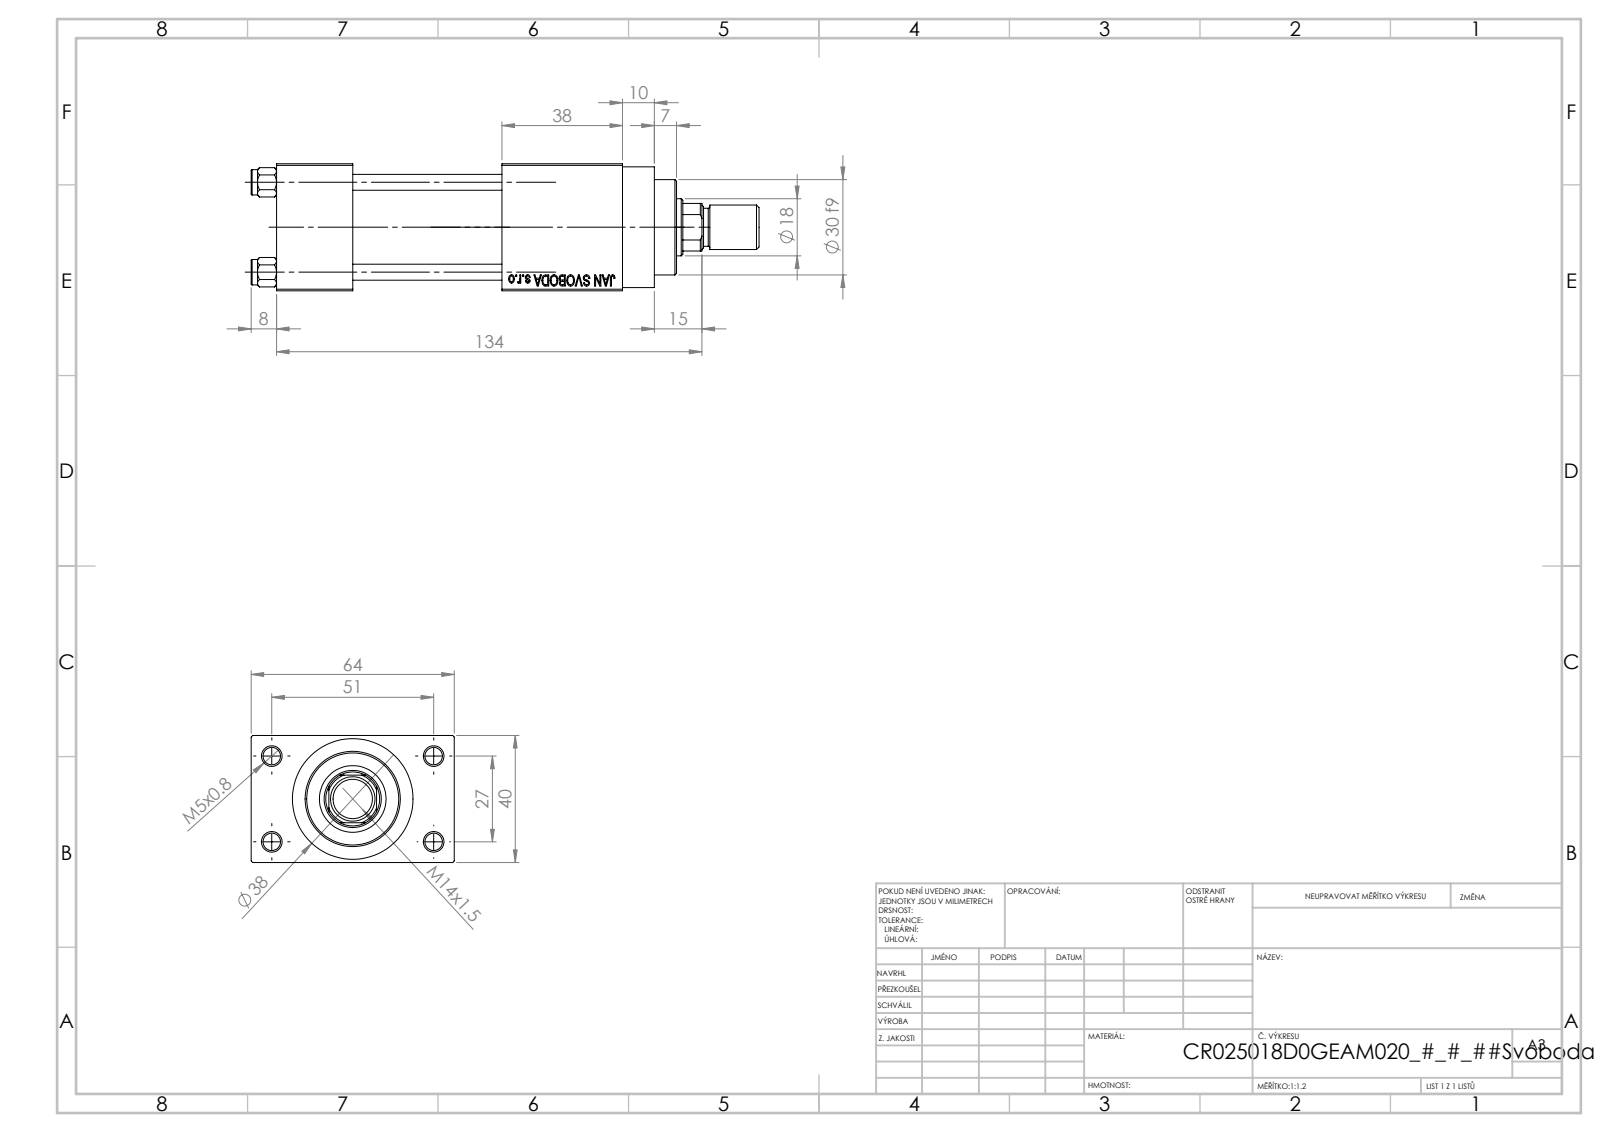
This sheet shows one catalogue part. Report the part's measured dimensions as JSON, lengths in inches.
{"part_name": "ROD_END_AH; NUT_M5_D; V215CR_VCP_D; V215_VC_A (+2 more)", "step_written_by": "SolidWorks 2019 (CONFIG_CONTROL_DESIGN)", "units": "inches", "bodies": {"solids": 12, "faces": 1114, "planar": 499, "cylindrical": 91, "other": 524}, "overall_size": [6.299, 2.52, 1.575], "volume_in3": 11.2, "surface_area_in2": 101.3, "round_holes": [[0.197, 4], [0.217, 4], [0.787, 3], [0.276, 2], [0.518, 2], [0.335, 1], [0.709, 1], [0.827, 1], [0.984, 1], [1.181, 1]], "round_bosses_or_shafts": [[0.315, 4], [1.496, 1], [1.22, 1], [0.551, 1], [0.472, 1]], "partial_cylinders_radius": [[0.335, 1]], "face_to_face_distances": [1.575, 0.472, 2.047, 1.85, 0.945, 2.795, 2.52, 1.496, 4.291, 3.346], "hole_center_spacings": [0.448, 0.788, 1.114, 1.136, 1.177, 1.561, 1.903, 1.063]}
